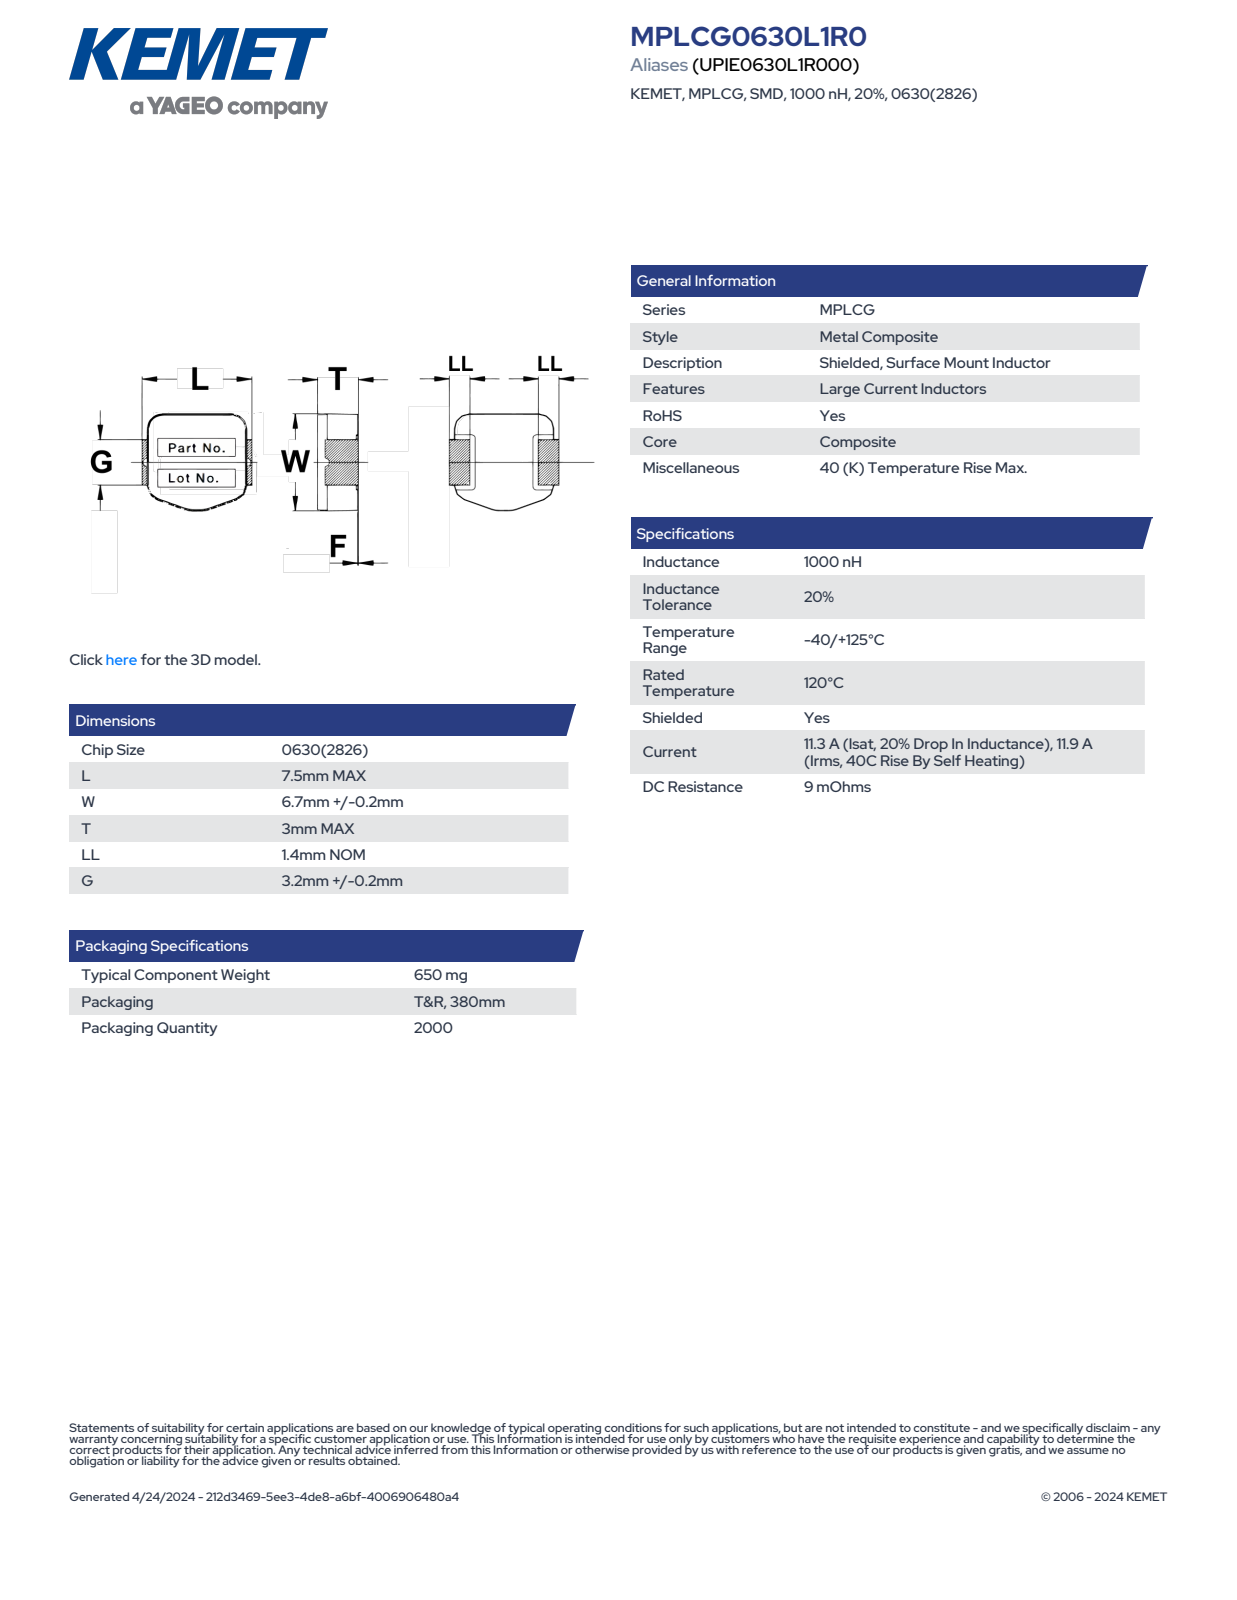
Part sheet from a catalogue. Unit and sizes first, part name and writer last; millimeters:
Units: millimetres
Overall size (bounding box): 7.5 × 6.9 × 3
Partial cylindrical surfaces — rounded edges, fillets, slot ends (radius × count): R1 ×4, R0.6 ×2, R0.15 ×1
Main face-to-face distances: 3, 7.3, 2.9, 7.1, 7.4, 7.2, 7.5, 6.9, 2.7, 3.01
Volume: 134 mm³ · Surface area: 194 mm²
Bodies: 4 solids, 116 faces (95 planar, 21 cylindrical, 0 other)
Part name (STEP PRODUCT): IS_MPLCG_3026_L7.5W6.9T3LL1.4F0.1G3.4
STEP written by: SolidWorks 2014 (AUTOMOTIVE_DESIGN)
